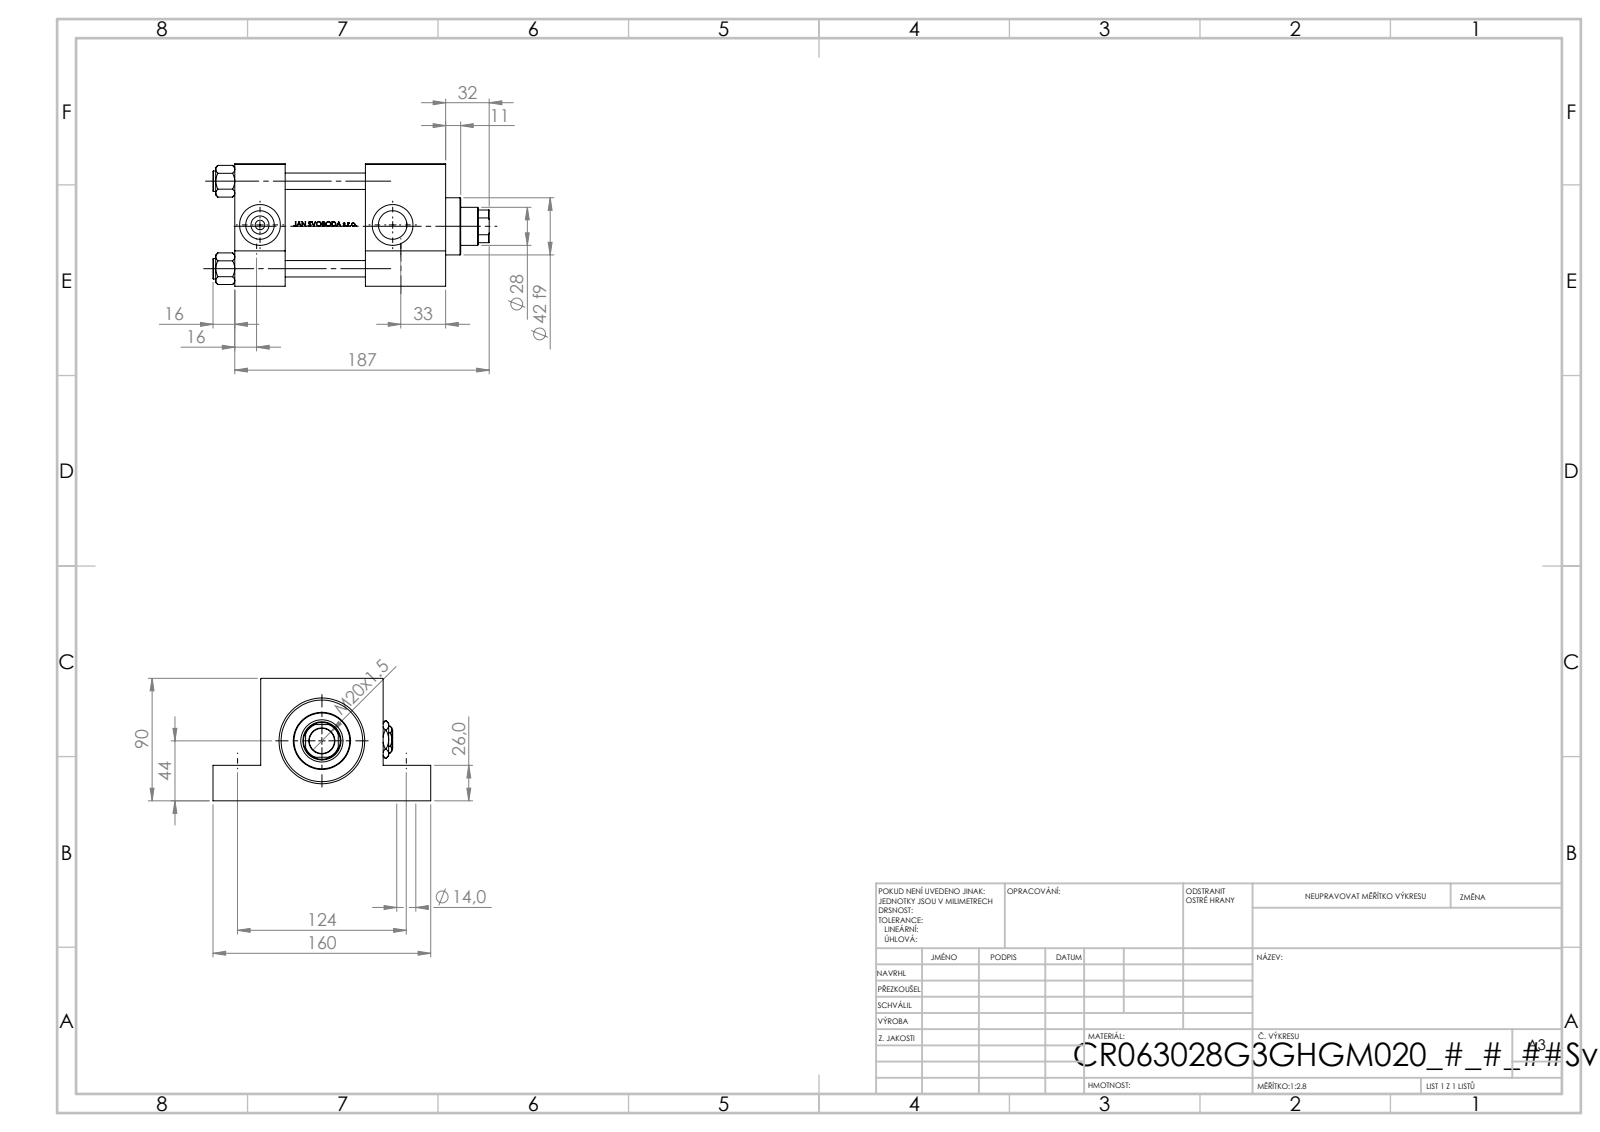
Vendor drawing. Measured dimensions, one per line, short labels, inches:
name: V215CR_G_Body; V215CR_G_TYCINKA; NUT_M5_G; V215_VC_A (+2 more)
written by: SolidWorks 2019 (CONFIG_CONTROL_DESIGN)
unit: in
bodies: 13 solids, 1184 faces (478 planar, 132 cylindrical, 574 other)
size: 7.992 × 6.299 × 3.543
volume: 67.74 in³; area: 316.7 in²
holes: 4× ⌀0.472, 4× ⌀0.551, 2× ⌀0.276, 2× ⌀0.825, 2× ⌀1.181, 1× ⌀0.728, 1× ⌀1.102, 1× ⌀1.22, 1× ⌀1.969, 1× ⌀2.362, 1× ⌀2.48
bosses: 4× ⌀0.591, 1× ⌀2.717, 1× ⌀1.654
rounds: 1× R0.531
face distances: 3.543, 2.323, 1.457, 4.646, 6.102, 3.78, 2.52, 1.024, 4.921, 1.378
hole spacings: 2.531, 1.763, 1.818, 3.58, 4.173, 4.882, 6.422, 3.839
